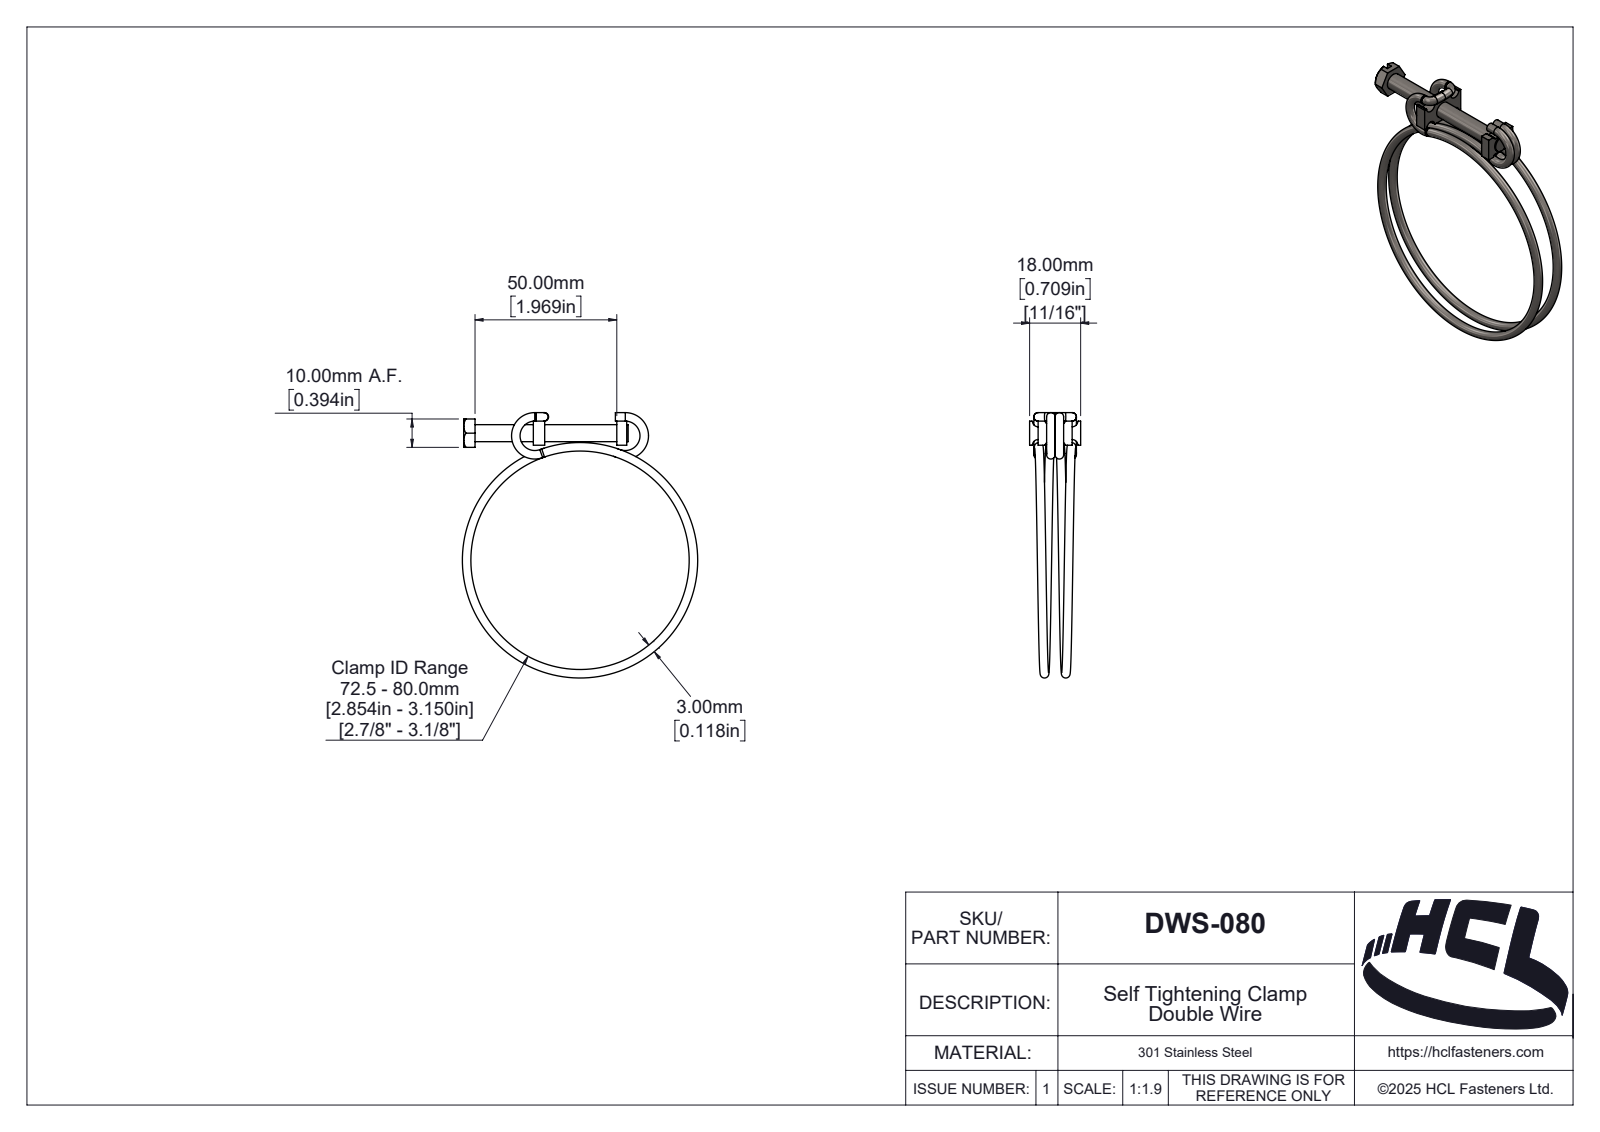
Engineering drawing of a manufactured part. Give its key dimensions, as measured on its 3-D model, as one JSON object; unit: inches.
{"part_name": "DWS-080", "step_written_by": "SolidWorks 2025 (AUTOMOTIVE_DESIGN)", "units": "inches", "bodies": {"solids": 6, "faces": 213, "planar": 55, "cylindrical": 74, "other": 84}, "overall_size": [3.683, 3.268, 0.709], "volume_in3": 0.44, "surface_area_in2": 13.35, "round_holes": [[0.236, 1]], "round_bosses_or_shafts": [[0.118, 4]], "partial_cylinders_radius": [[0.008, 12], [0.039, 4], [0.079, 4], [0.016, 1], [0.02, 1], [0.021, 1], [0.025, 1], [0.036, 1]], "face_to_face_distances": [0.157, 0.967, 0.394, 1.159, 0.118, 2.126, 1.139, 2.106, 0.039, 1.002]}
